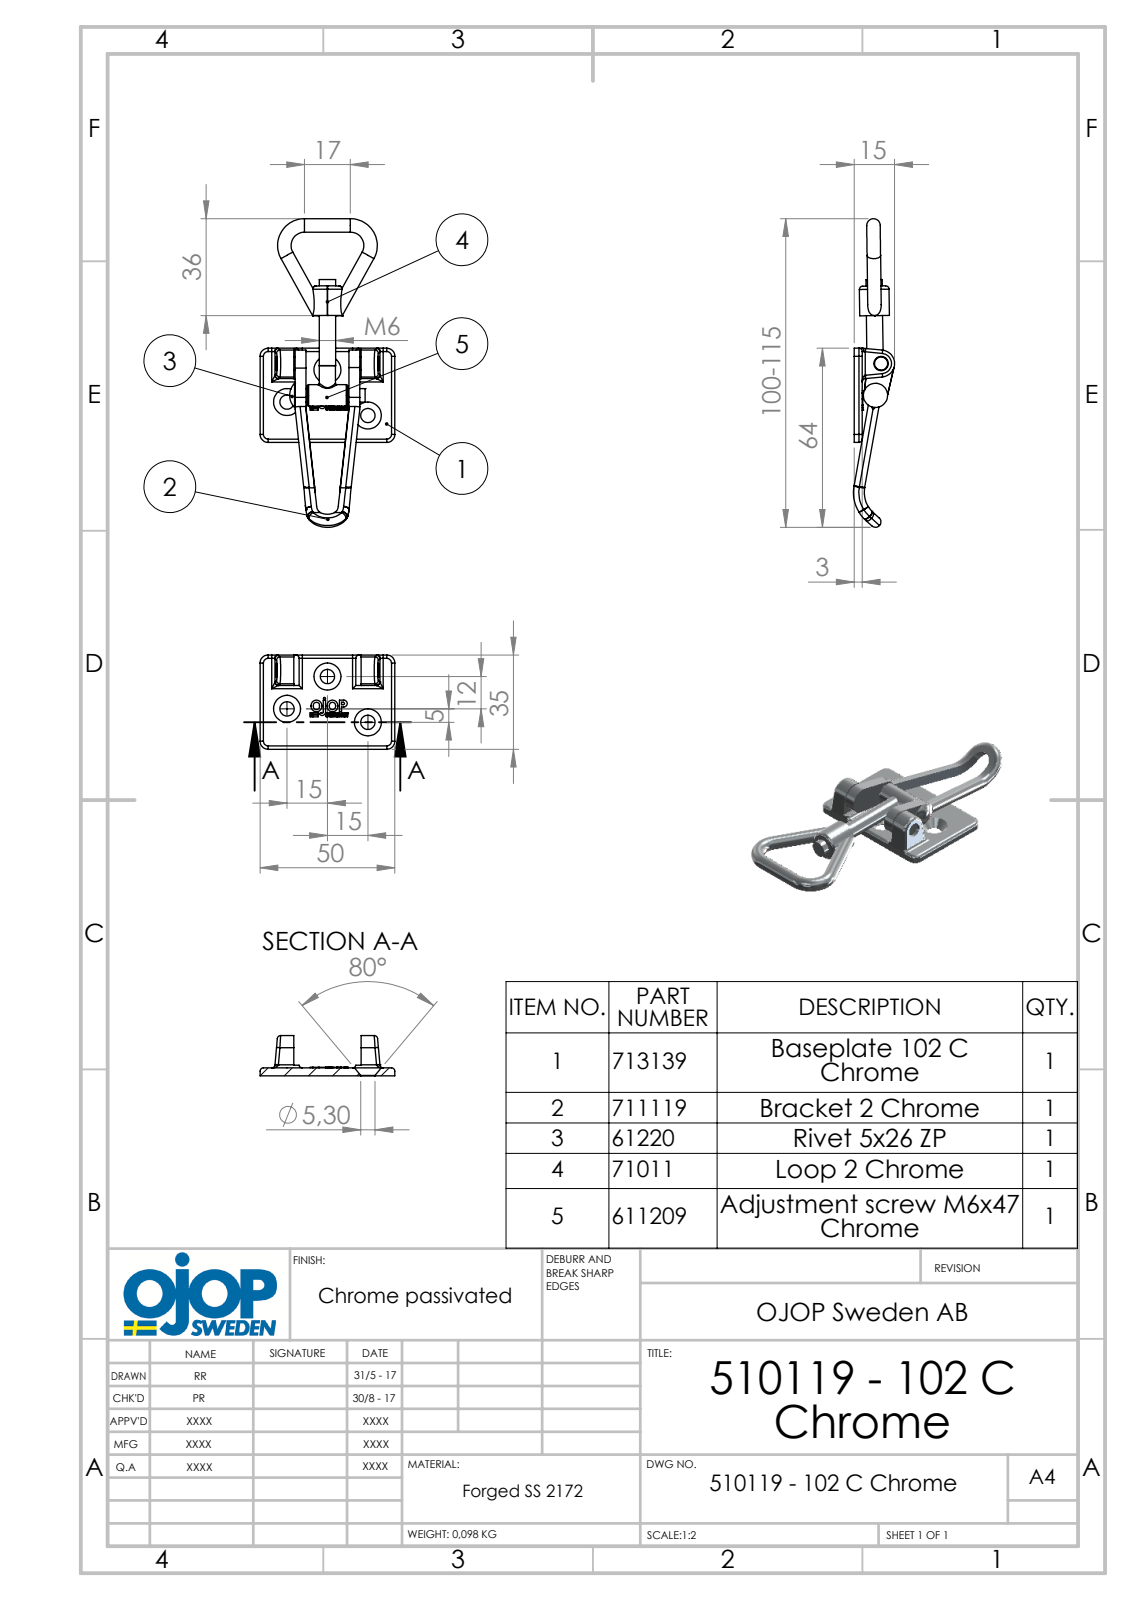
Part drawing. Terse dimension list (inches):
name: 102 C; 510119 - 102 C Kromad; bygel 2; Hålnit 5x26 (+2 more)
written by: SolidWorks 2015 (AUTOMOTIVE_DESIGN)
unit: in
bodies: 5 solids, 218 faces (51 planar, 85 cylindrical, 82 other)
size: 4.774 × 1.969 × 0.652
volume: 0.835 in³; area: 17.7 in²
holes: 4× ⌀0.209, 1× ⌀0.079, 1× ⌀0.205, 1× ⌀0.24
bosses: 4× ⌀0.197, 1× ⌀0.354, 1× ⌀0.315, 1× ⌀0.237, 1× ⌀0.236, 1× ⌀0.191
rounds: 15× R0.049, 4× R0.079, 4× R0.118, 4× R0.216, 1× R0.157, 1× R0.197, 1× R0.207, 1× R0.787
face distances: 0.118, 0.157, 0.787, 0.02, 0.177, 0.63, 0.945, 0.807, 0.965, 0.492
hole spacings: 0.472, 0.756, 0.893, 1.197
